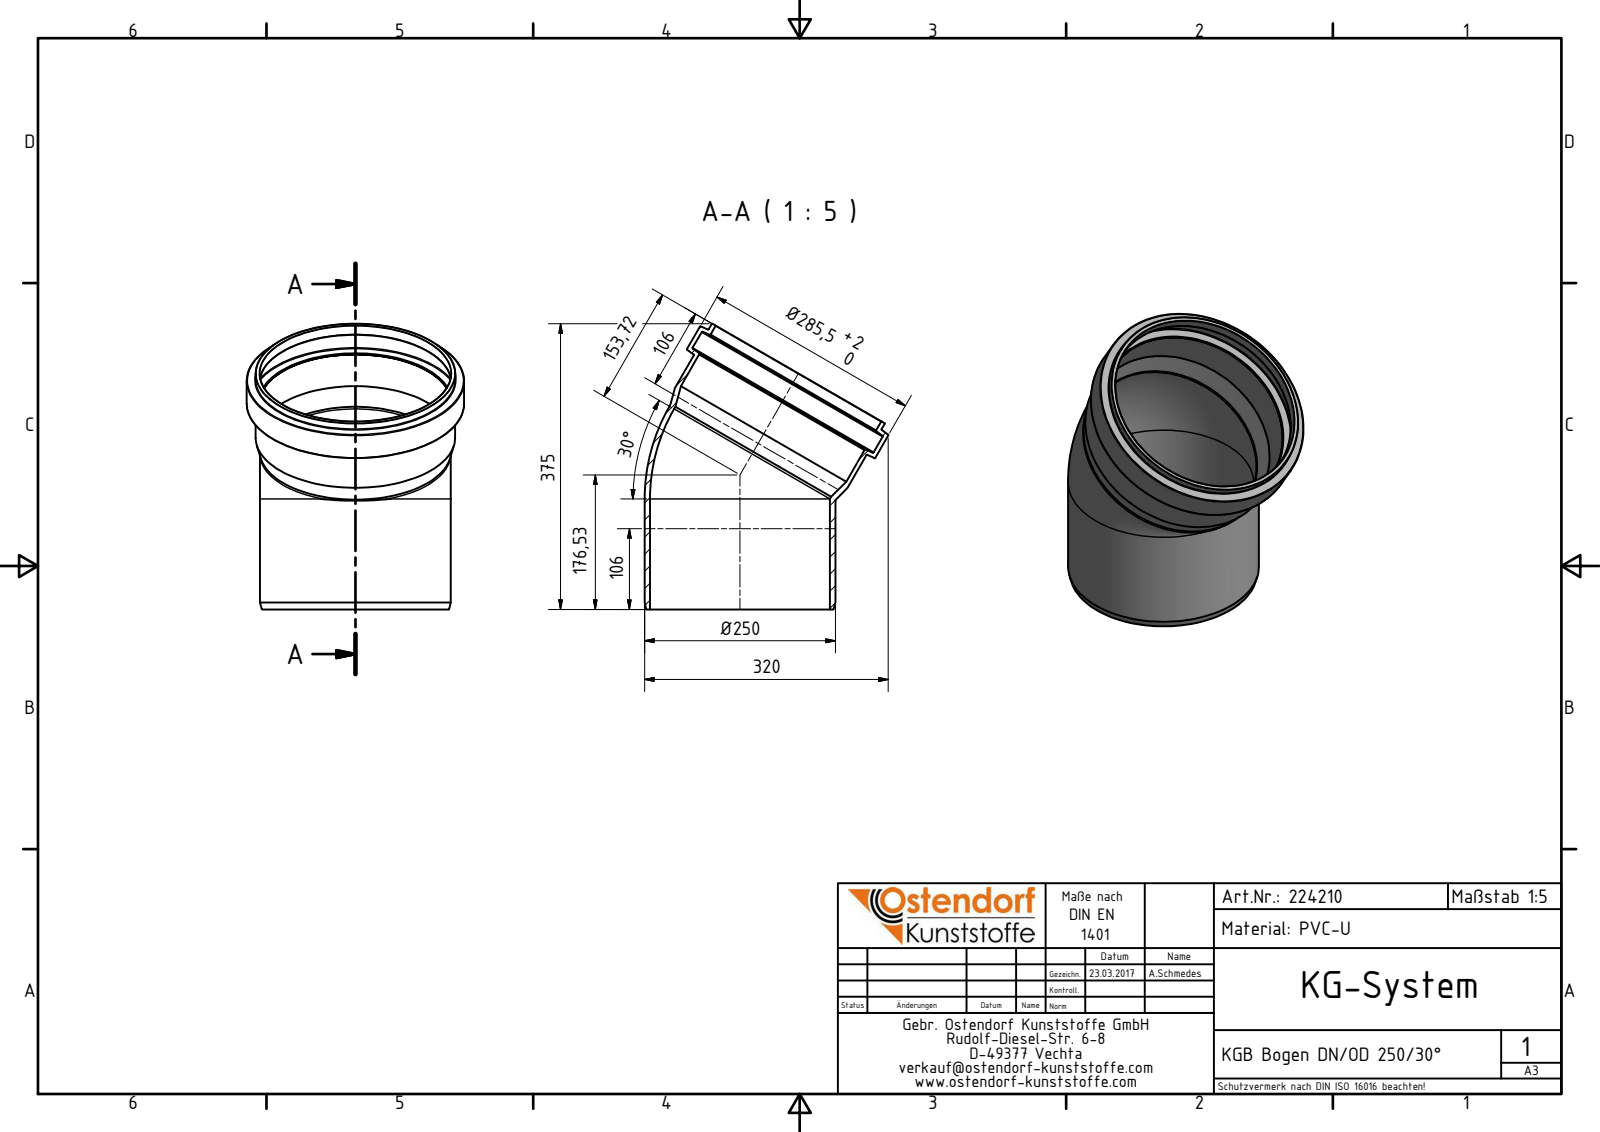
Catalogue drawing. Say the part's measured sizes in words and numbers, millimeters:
The part is named "224210 KGB Bogen DN_OD 250_30°". Its 3-D file was written by "Autodesk Inventor 2016 (AUTOMOTIVE_DESIGN)". It is 1 solid with 34 faces: 3 planar, 11 cylindrical and 20 other. Overall it measures 375 by 320 by 285.5 millimeters. Its volume is 1 708 000 cubic millimeters and its surface area 559 065 square millimeters. Round holes: 2 of diameter 236.3, 1 of diameter 250.8, 1 of diameter 251.1, 1 of diameter 274.5. Round bosses or shafts: 2 of diameter 250.5, 1 of diameter 285.5, 1 of diameter 262.1, 1 of diameter 261.8. The main face-to-face distances are 43.63.
